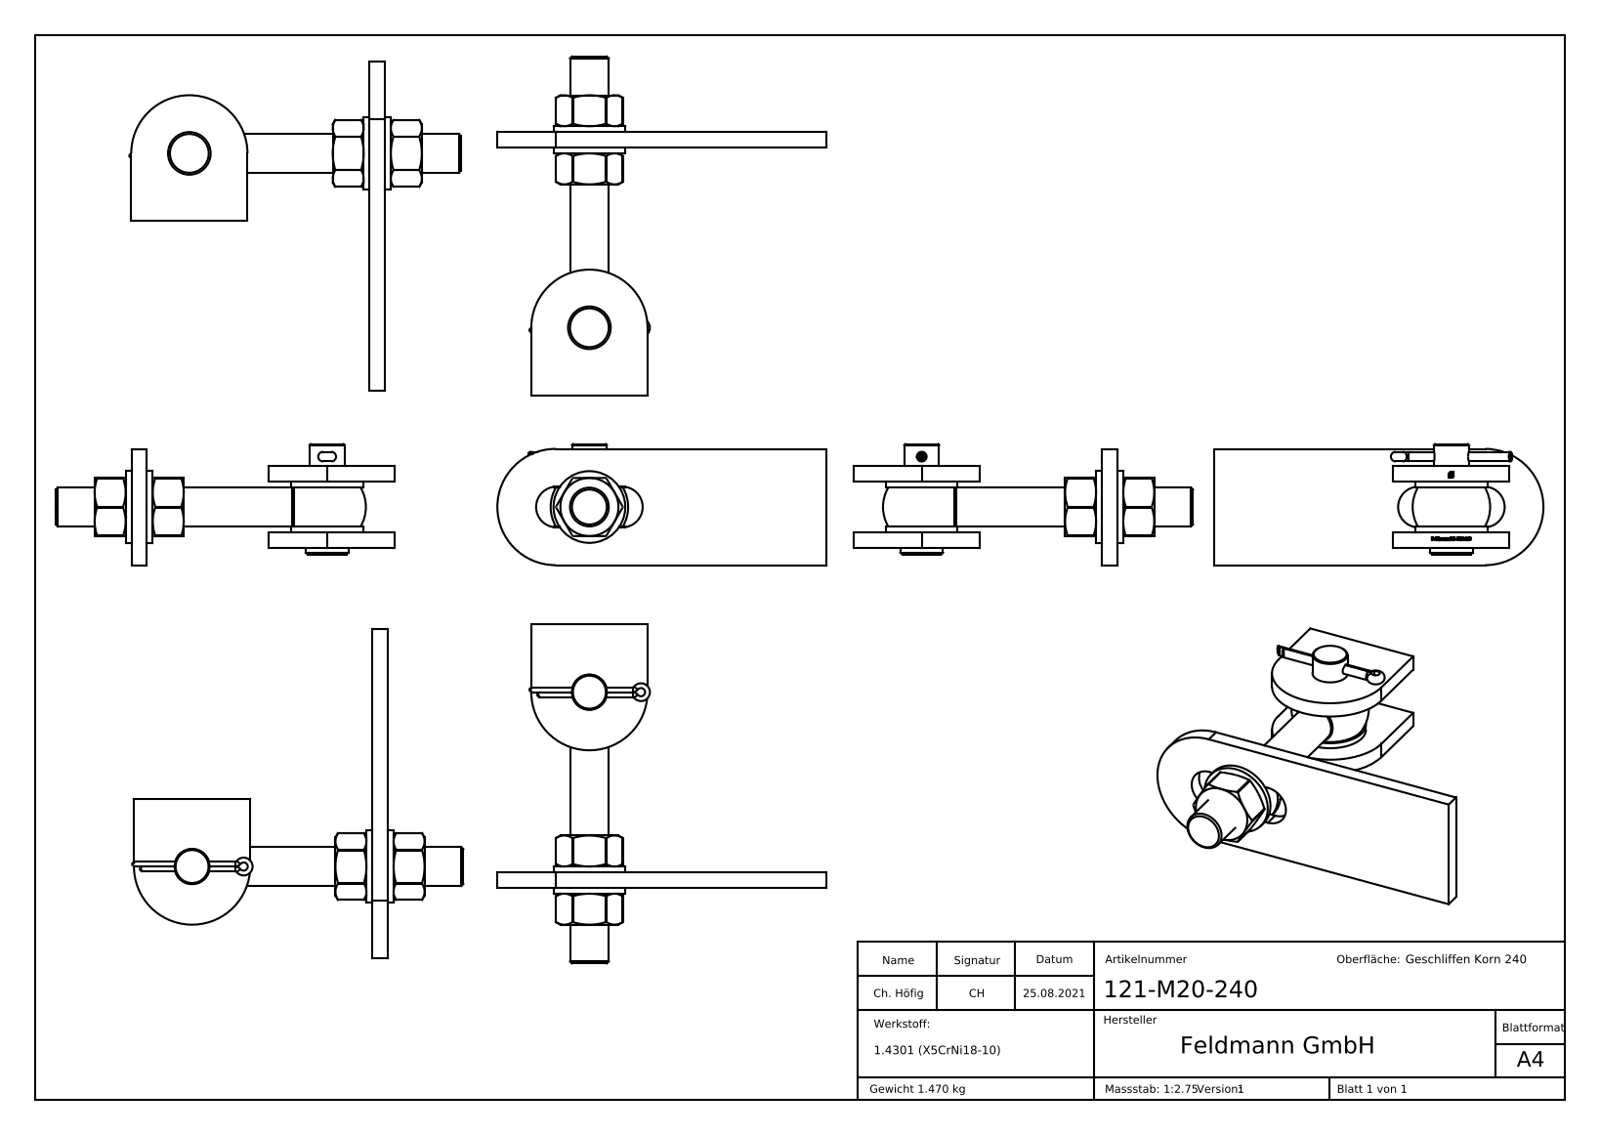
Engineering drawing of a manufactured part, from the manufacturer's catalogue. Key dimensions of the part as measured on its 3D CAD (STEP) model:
Part name (STEP PRODUCT): 121-MXX-XXX Teil2; 121-MXX-XXX Teil5; 121-MXX-XXX Teil1_121-M20-240 Teil1; DIN 934 M4-M20_DIN 934 M20 (+8 more)
STEP written by: SolidWorks 2018 (CONFIG_CONTROL_DESIGN)
Units: millimetres
Bodies: 12 solids, 636 faces (359 planar, 41 cylindrical, 236 other)
Overall size (bounding box): 24000 × 14000.03 × 14000
Volume: 219 588 mm³ · Surface area: 73 069 mm²
Round holes (diameter × count): ⌀21 ×2, ⌀17.5 ×1, ⌀18.2 ×1
Round bosses / shafts (diameter × count): ⌀37 ×2, ⌀22 ×1, ⌀20 ×1, ⌀18 ×1, ⌀5 ×1
Partial cylindrical surfaces — rounded edges, fillets, slot ends (radius × count): R0.5 ×6, R1 ×2, R3.49 ×2, R10.5 ×2, R30 ×2, R2.11 ×1
Main face-to-face distances: 8, 34, 3, 11, 26, 20, 42, 31, 23, 43
